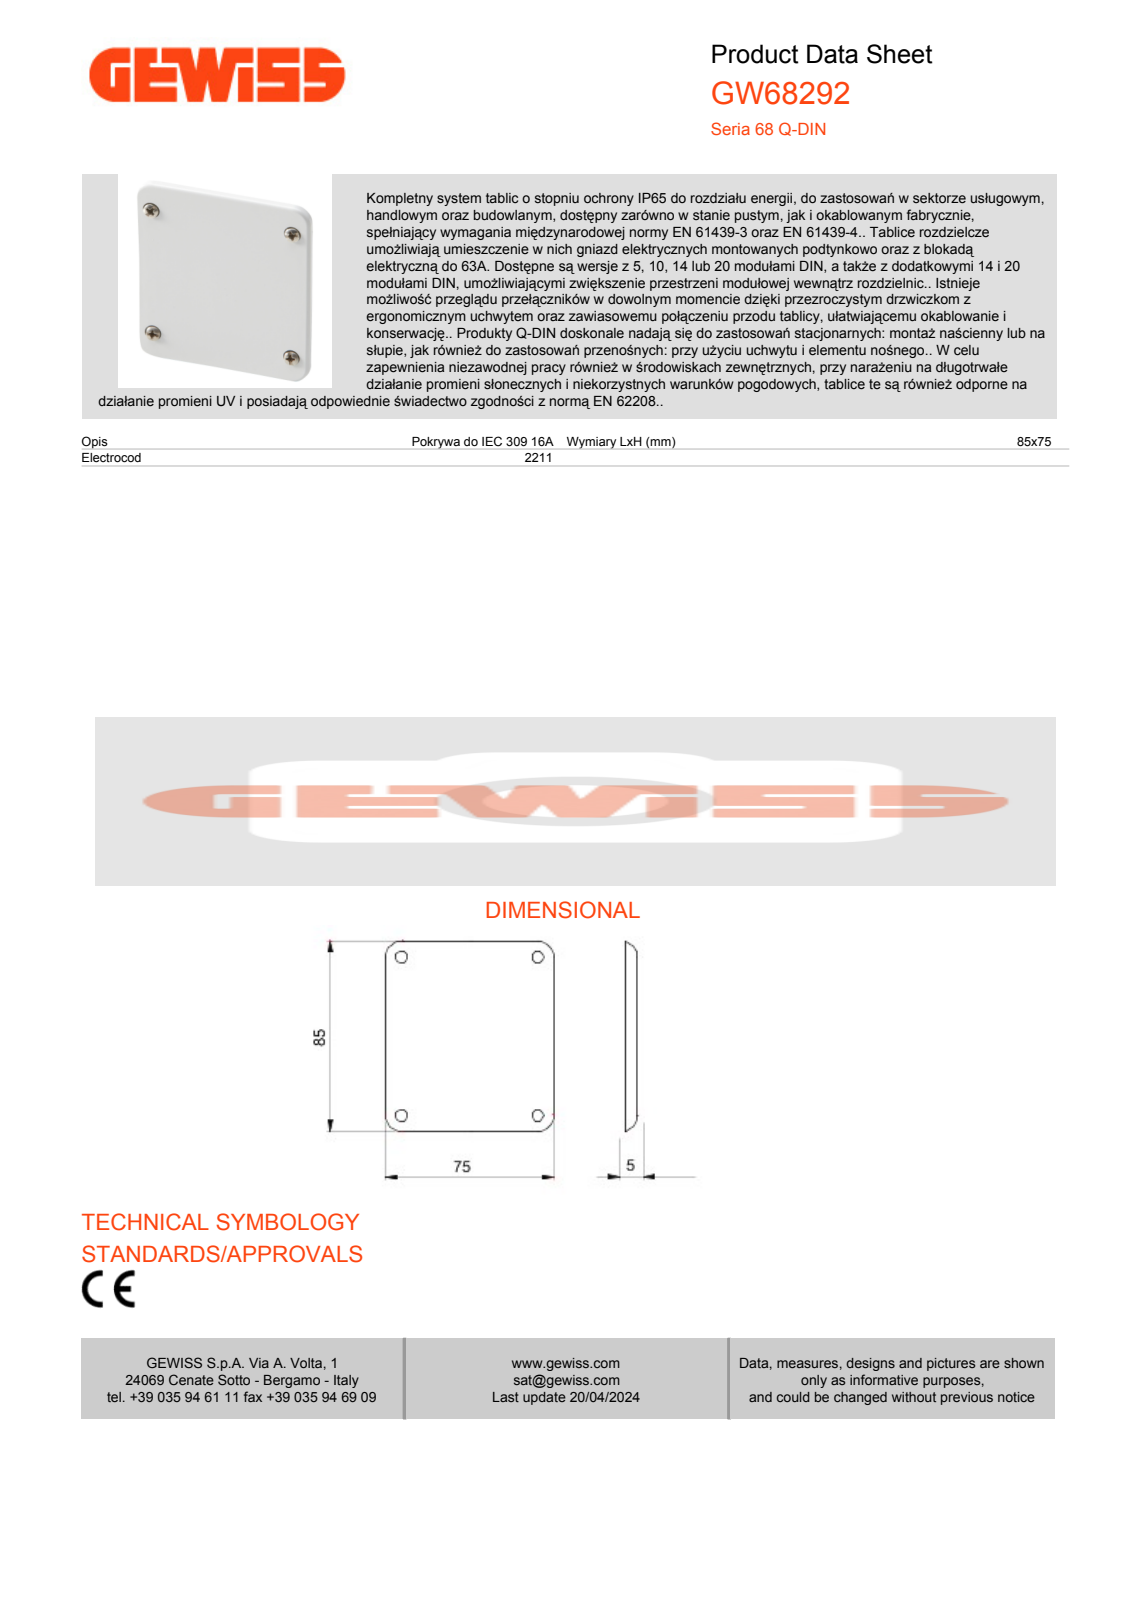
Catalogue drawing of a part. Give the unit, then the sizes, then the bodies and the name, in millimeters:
Units: millimetres
Overall size (bounding box): 85 × 75 × 12
Round holes (diameter × count): ⌀4 ×4, ⌀7 ×4
Round bosses / shafts (diameter × count): ⌀1.5 ×1
Partial cylindrical surfaces — rounded edges, fillets, slot ends (radius × count): R1.5 ×4, R2.8 ×4, R4 ×4, R5 ×4, R6.5 ×4, R8 ×4, R35.41 ×2, R36.6 ×2
Main face-to-face distances: 2, 1.5, 1.2, 4.3, 2.3, 3.5, 0.8, 2.5, 82, 0.5
Hole centre spacings: 60, 84.85
Volume: 14 514 mm³ · Surface area: 16 041 mm²
Bodies: 1 solid, 183 faces (121 planar, 58 cylindrical, 4 other)
Part name (STEP PRODUCT): GW68292
STEP written by: CREO PARAMETRIC BY PTC INC, 2020354 (CONFIG_CONTROL_DESIGN)
